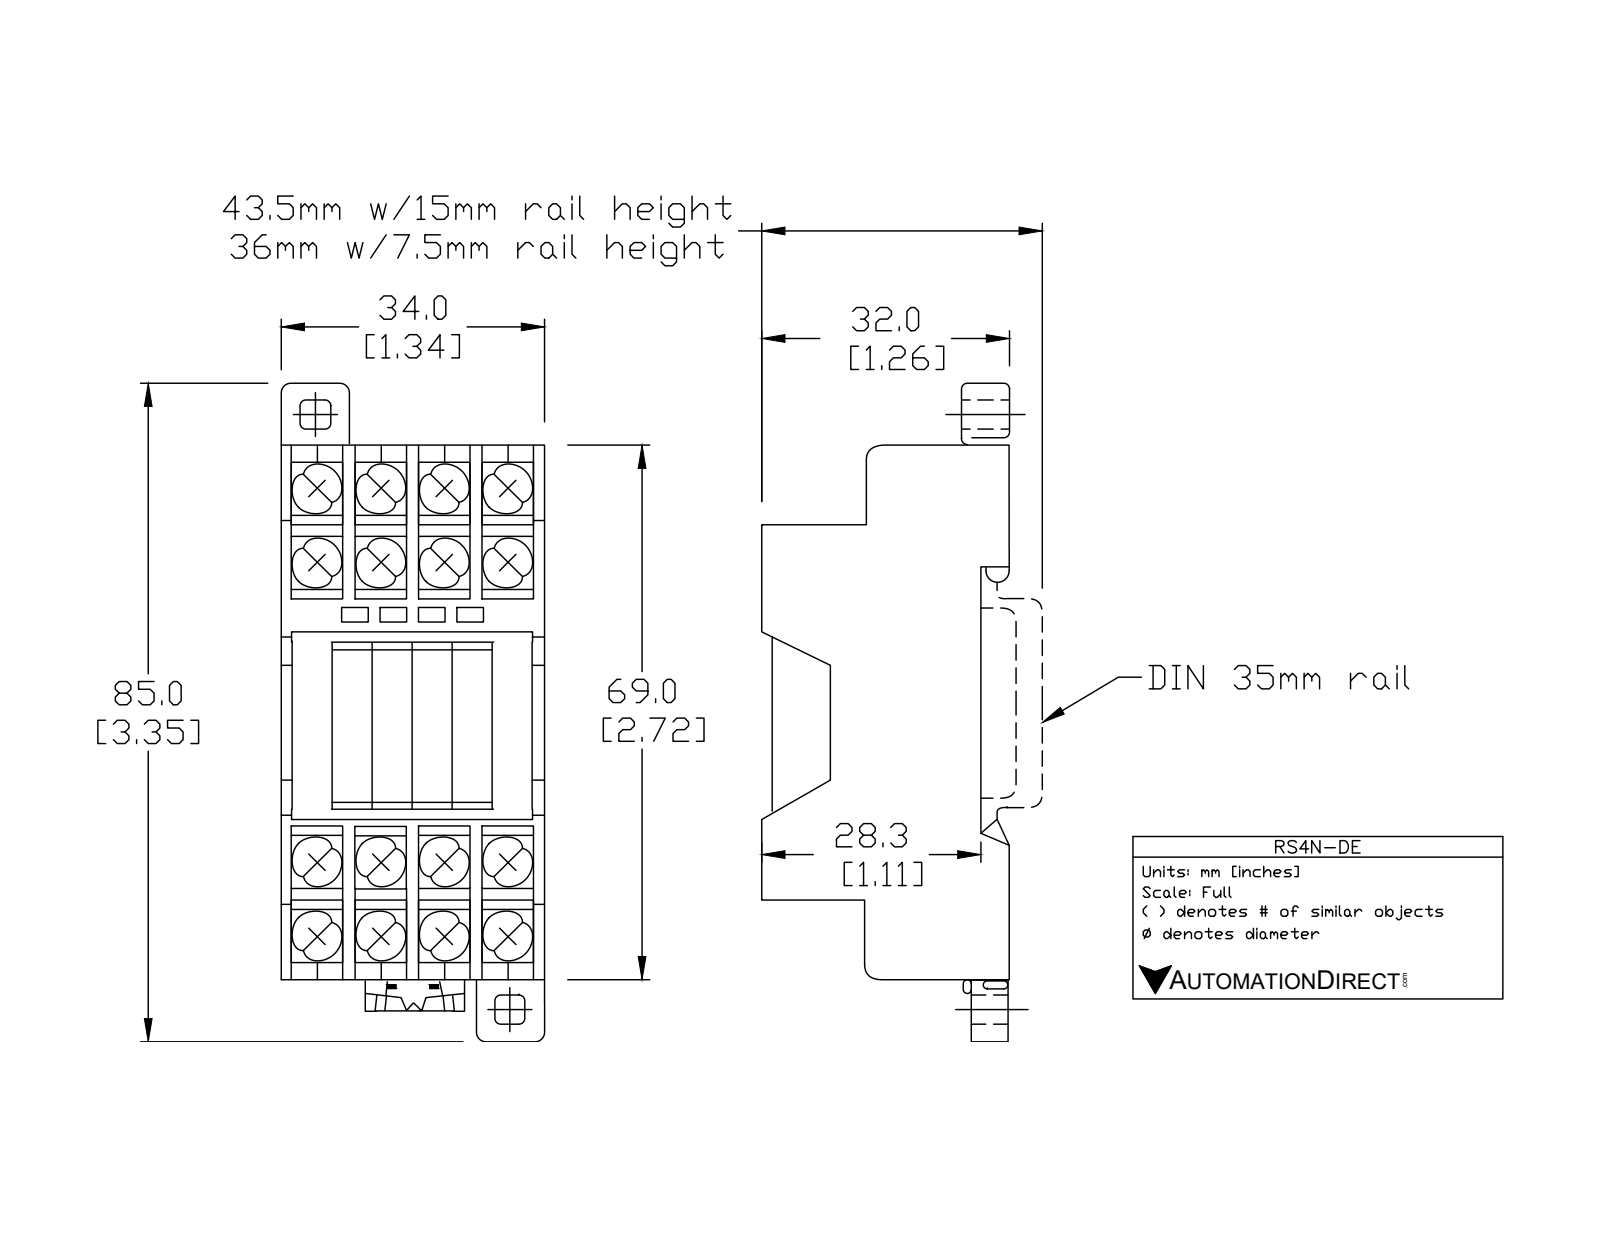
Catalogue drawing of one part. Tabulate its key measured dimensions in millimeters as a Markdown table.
| quantity | value |
| --- | --- |
| part name | RS4N-DE |
| STEP written by | SolidWorks 2013 (AUTOMOTIVE_DESIGN) |
| units | millimeters |
| bodies | 1 solid, 607 faces (520 planar, 55 cylindrical, 32 other) |
| overall size | 84.8 × 34 × 32 |
| volume | 46 820 mm³ |
| surface area | 19 340 mm² |
| round bosses / shafts (diameter × count) | 6.1 × 8, 6 × 8 |
| partial cylindrical surfaces (radius × count) | 0.8 × 8, 1 × 4, 2.5 × 2, 1 × 1 |
| main face-to-face distances | 1.5, 8.1, 34, 16.3, 8.1, 4.6, 12.7, 3.6, 8.6, 6.6 |
